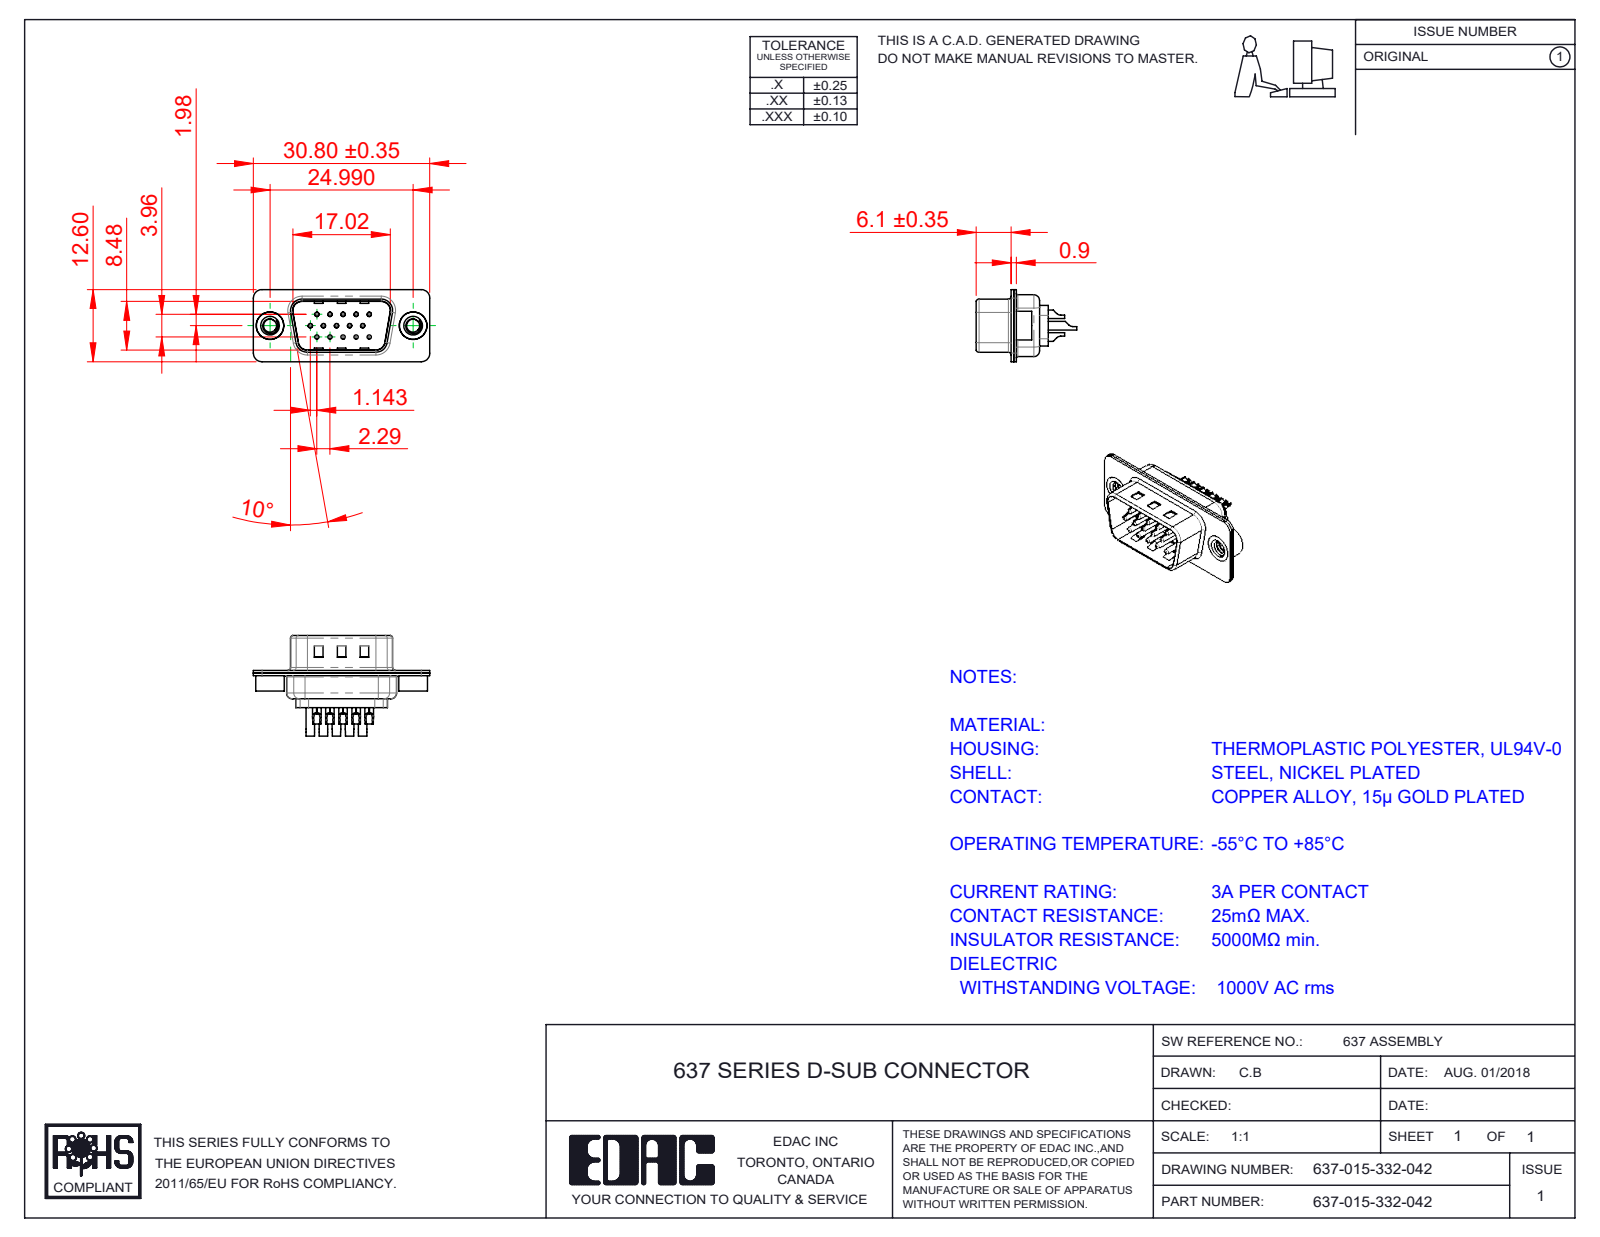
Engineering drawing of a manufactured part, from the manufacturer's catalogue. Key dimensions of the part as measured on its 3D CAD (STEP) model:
Part name (STEP PRODUCT): 637 Contact Row 1_32; 637-015-332-062; 637 Contact Row 3_32; 637 4-40 Threaded Rivet (+4 more)
STEP written by: SolidWorks 2020 (CONFIG_CONTROL_DESIGN)
Units: millimetres
Bodies: 20 solids, 1264 faces (317 planar, 564 cylindrical, 383 other)
Overall size (bounding box): 30.8 × 17.55 × 12.6
Volume: 1 332 mm³ · Surface area: 4 779 mm²
Round holes (diameter × count): ⌀0.35 ×15, ⌀1.1 ×15, ⌀1.6 ×15, ⌀2.26 ×2, ⌀4 ×2, ⌀4.8 ×2
Round bosses / shafts (diameter × count): ⌀2 ×15, ⌀1.5 ×15, ⌀0.75 ×15, ⌀5 ×2, ⌀4.9 ×2
Partial cylindrical surfaces — rounded edges, fillets, slot ends (radius × count): R1.5 ×16, R2 ×12, R0.5 ×8, R1 ×7, R0.25 ×4, R0.55 ×4, R0.7 ×4, R0.95 ×4
Main face-to-face distances: 0.45, 0.9, 0.4, 0.7, 8.88, 8.48, 1.05, 0.31, 4.55, 1.16
Hole centre spacings: 3.96, 2.28, 4.57, 2.29, 6.05, 6.86, 7.92, 6.04
